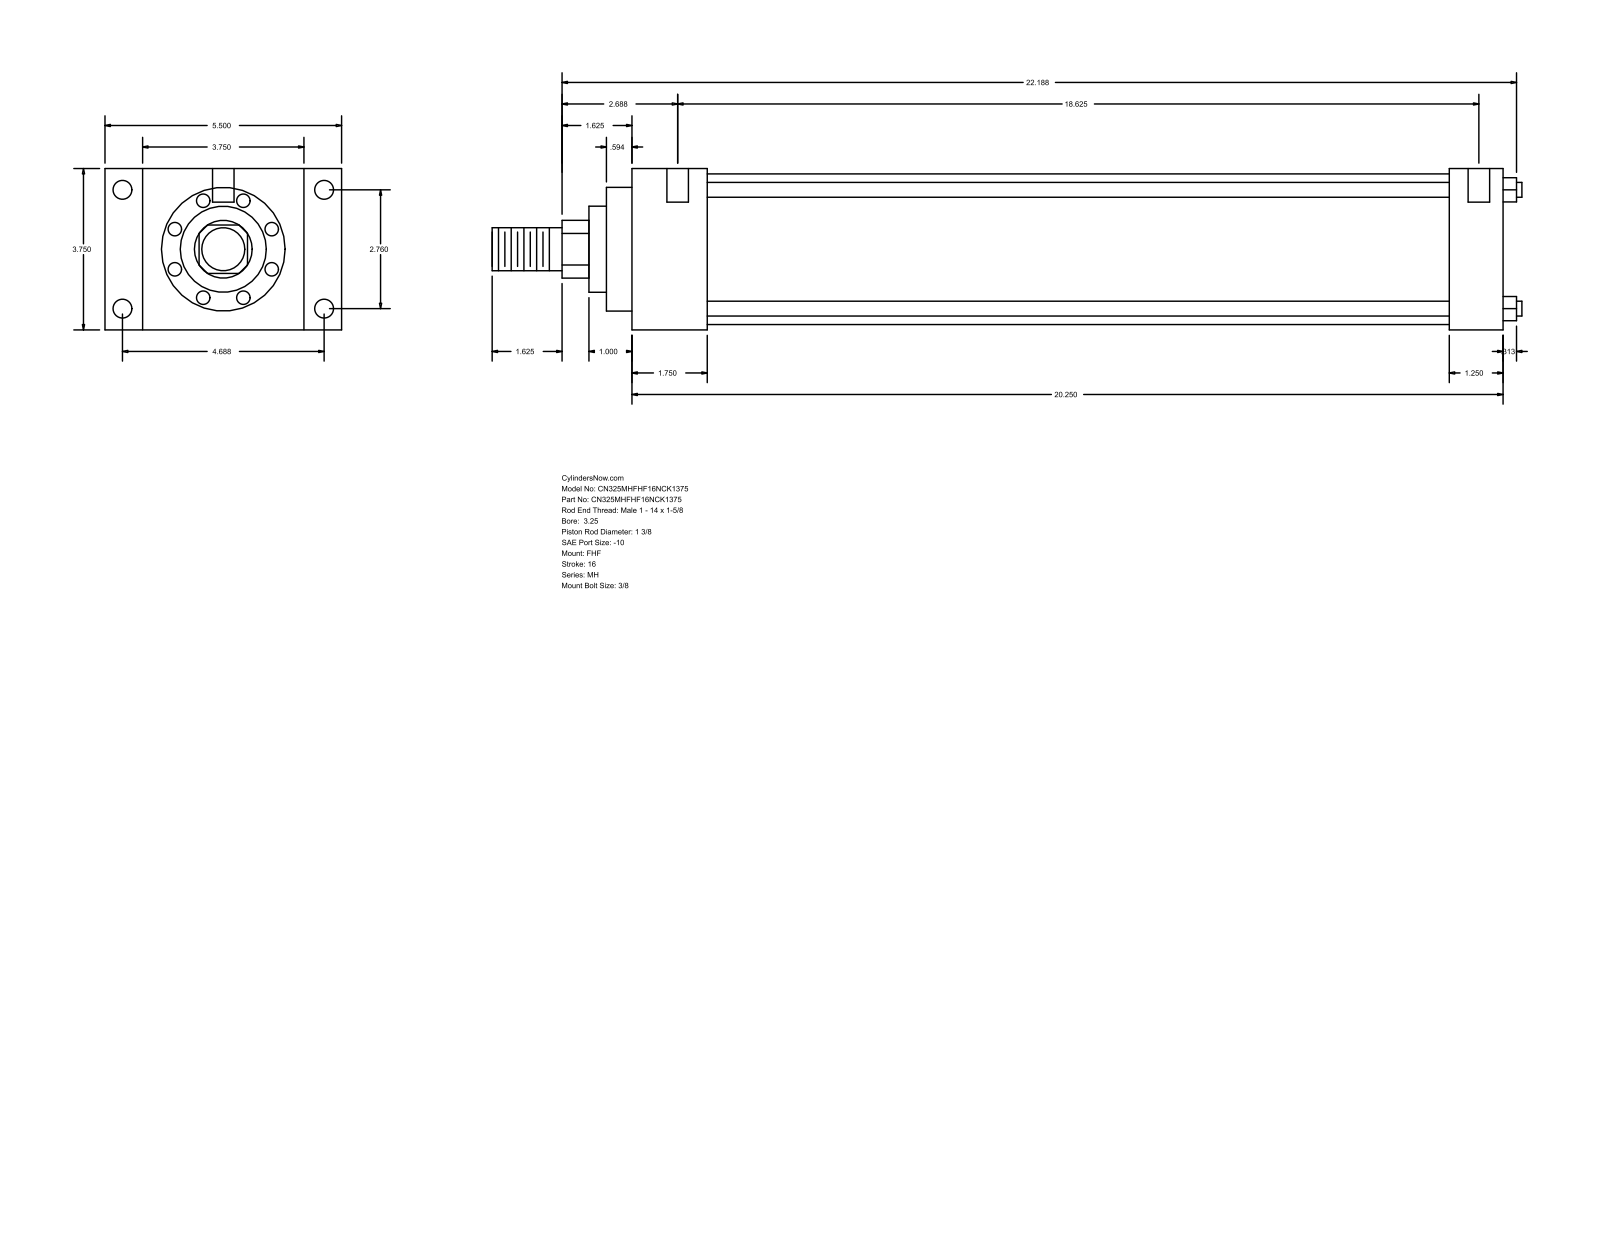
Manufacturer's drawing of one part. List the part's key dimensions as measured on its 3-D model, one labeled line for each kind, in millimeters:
Part name (STEP PRODUCT): MH_FHF__0325_1.375
STEP written by: GSSL Pune (CONFIG_CONTROL_DESIGN)
Units: millimetres
Bodies: 0 solids, 90 faces (61 planar, 29 cylindrical, 0 other)
Overall size (bounding box): 608.01 × 139.7 × 95.25
Round holes (diameter × count): ⌀5.56 ×4, ⌀11.13 ×4, ⌀12.7 ×2
Round bosses / shafts (diameter × count): ⌀8.76 ×4, ⌀88.9 ×1, ⌀73.03 ×1, ⌀50.8 ×1, ⌀34.92 ×1, ⌀25.4 ×1
Partial cylindrical surfaces — rounded edges, fillets, slot ends (radius × count): R17.06 ×1
Main face-to-face distances: 95.24, 514.35, 44.45, 469.9, 22.23, 117.47, 139.7, 482.61, 438.16, 31.74
Hole centre spacings: 70.1, 119.06, 138.16, 479.43, 1.59, 4.76, 473.08, 474.67
